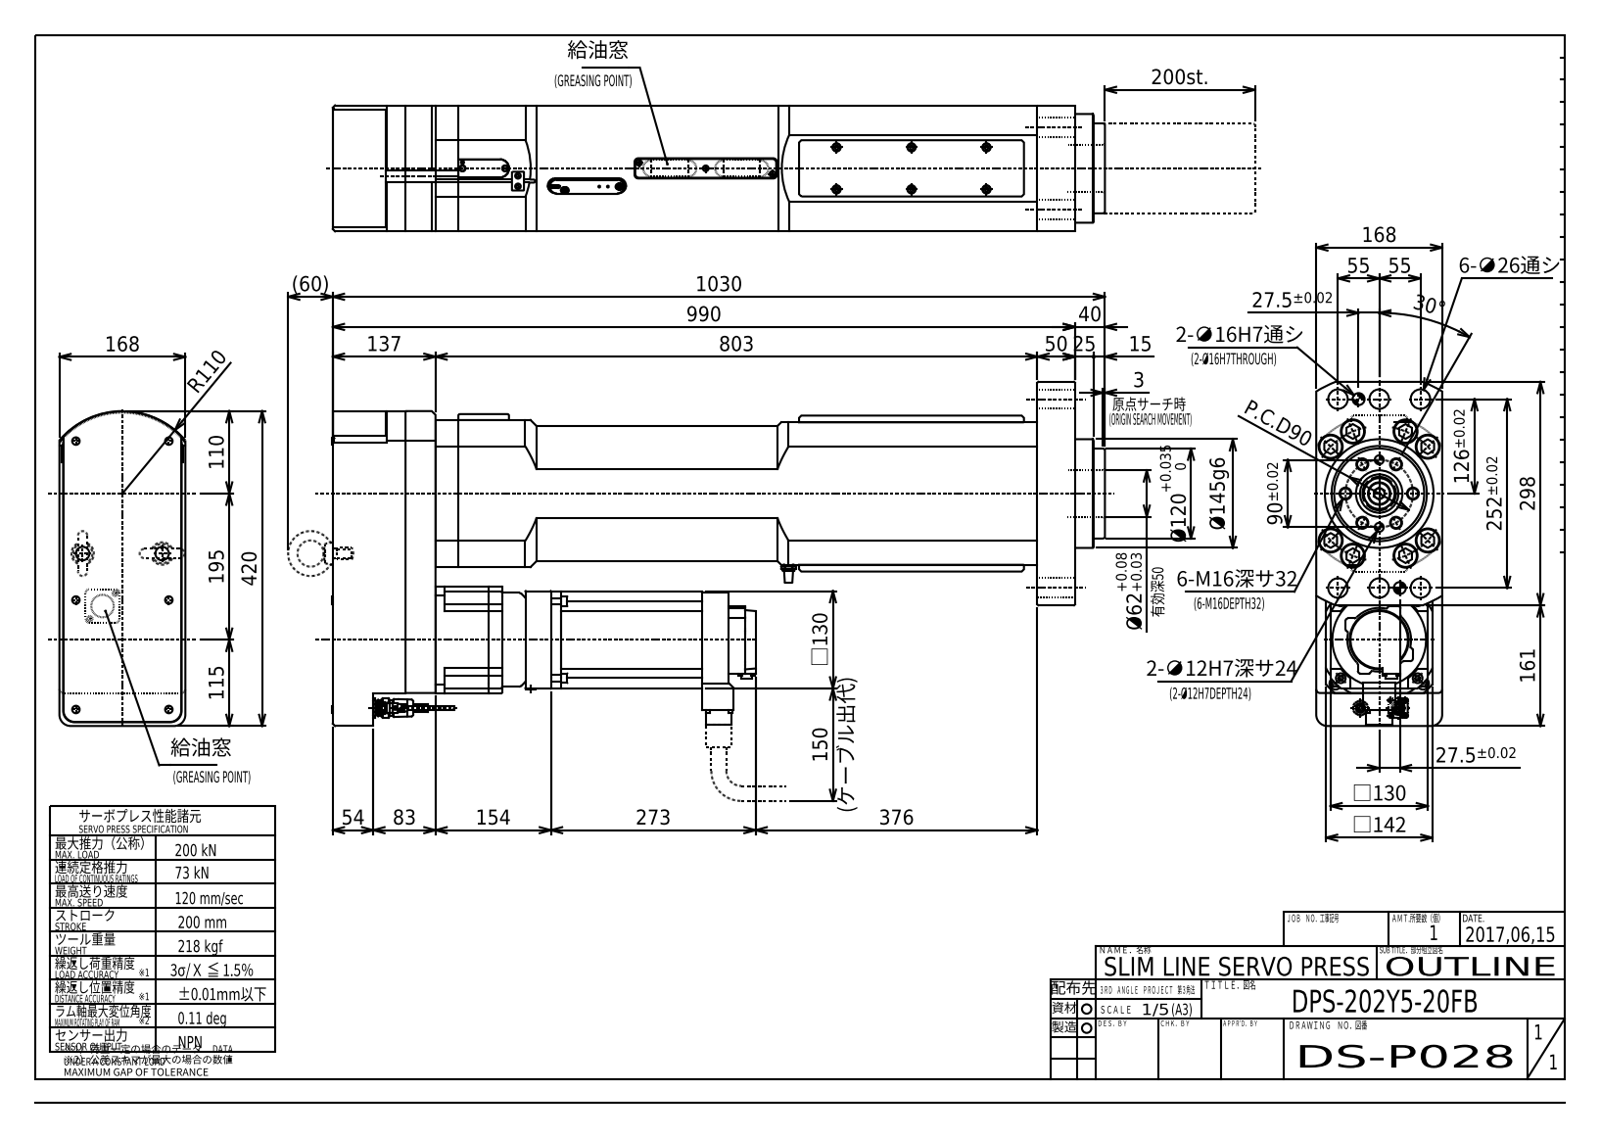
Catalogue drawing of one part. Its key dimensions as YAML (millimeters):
part_name: "DPS-202Y5-20FB(DS-P028)_OUTLINE; DS-P028-04"
step_written_by: "Autodesk Inventor 2017 (AUTOMOTIVE_DESIGN)"
units: millimeters
bodies: {solids: 2, faces: 1703, planar: 877, cylindrical: 422, other: 404}
overall_size: [1089.6, 459, 168]
volume: 39880000
surface_area: 1616000
round_holes:
  - {diameter: 10.11, count: 8}
  - {diameter: 32, count: 8}
  - {diameter: 7, count: 6}
  - {diameter: 11, count: 6}
  - {diameter: 13.84, count: 6}
  - {diameter: 26, count: 6}
  - {diameter: 3.24, count: 4}
  - {diameter: 9, count: 4}
  - {diameter: 4.5, count: 2}
  - {diameter: 8, count: 2}
  - {diameter: 12, count: 2}
  - {diameter: 14, count: 2}
round_bosses_or_shafts:
  - {diameter: 10, count: 12}
  - {diameter: 0.75, count: 10}
  - {diameter: 30, count: 9}
  - {diameter: 5, count: 9}
  - {diameter: 12, count: 8}
  - {diameter: 6, count: 6}
  - {diameter: 1, count: 6}
  - {diameter: 0.5, count: 5}
partial_cylinders:
  - {radius: 0.4, count: 24}
  - {radius: 5, count: 12}
  - {radius: 2, count: 10}
  - {radius: 4.5, count: 10}
  - {radius: 2.5, count: 8}
  - {radius: 3.4, count: 6}
  - {radius: 7, count: 6}
  - {radius: 15, count: 6}
face_to_face_distances: [168, 6, 19, 136, 149, 130, 162, 26.5, 26, 50]
hole_center_spacings: [257.93, 27.5, 35.88, 47.49, 55, 55.67, 64.22, 90]
